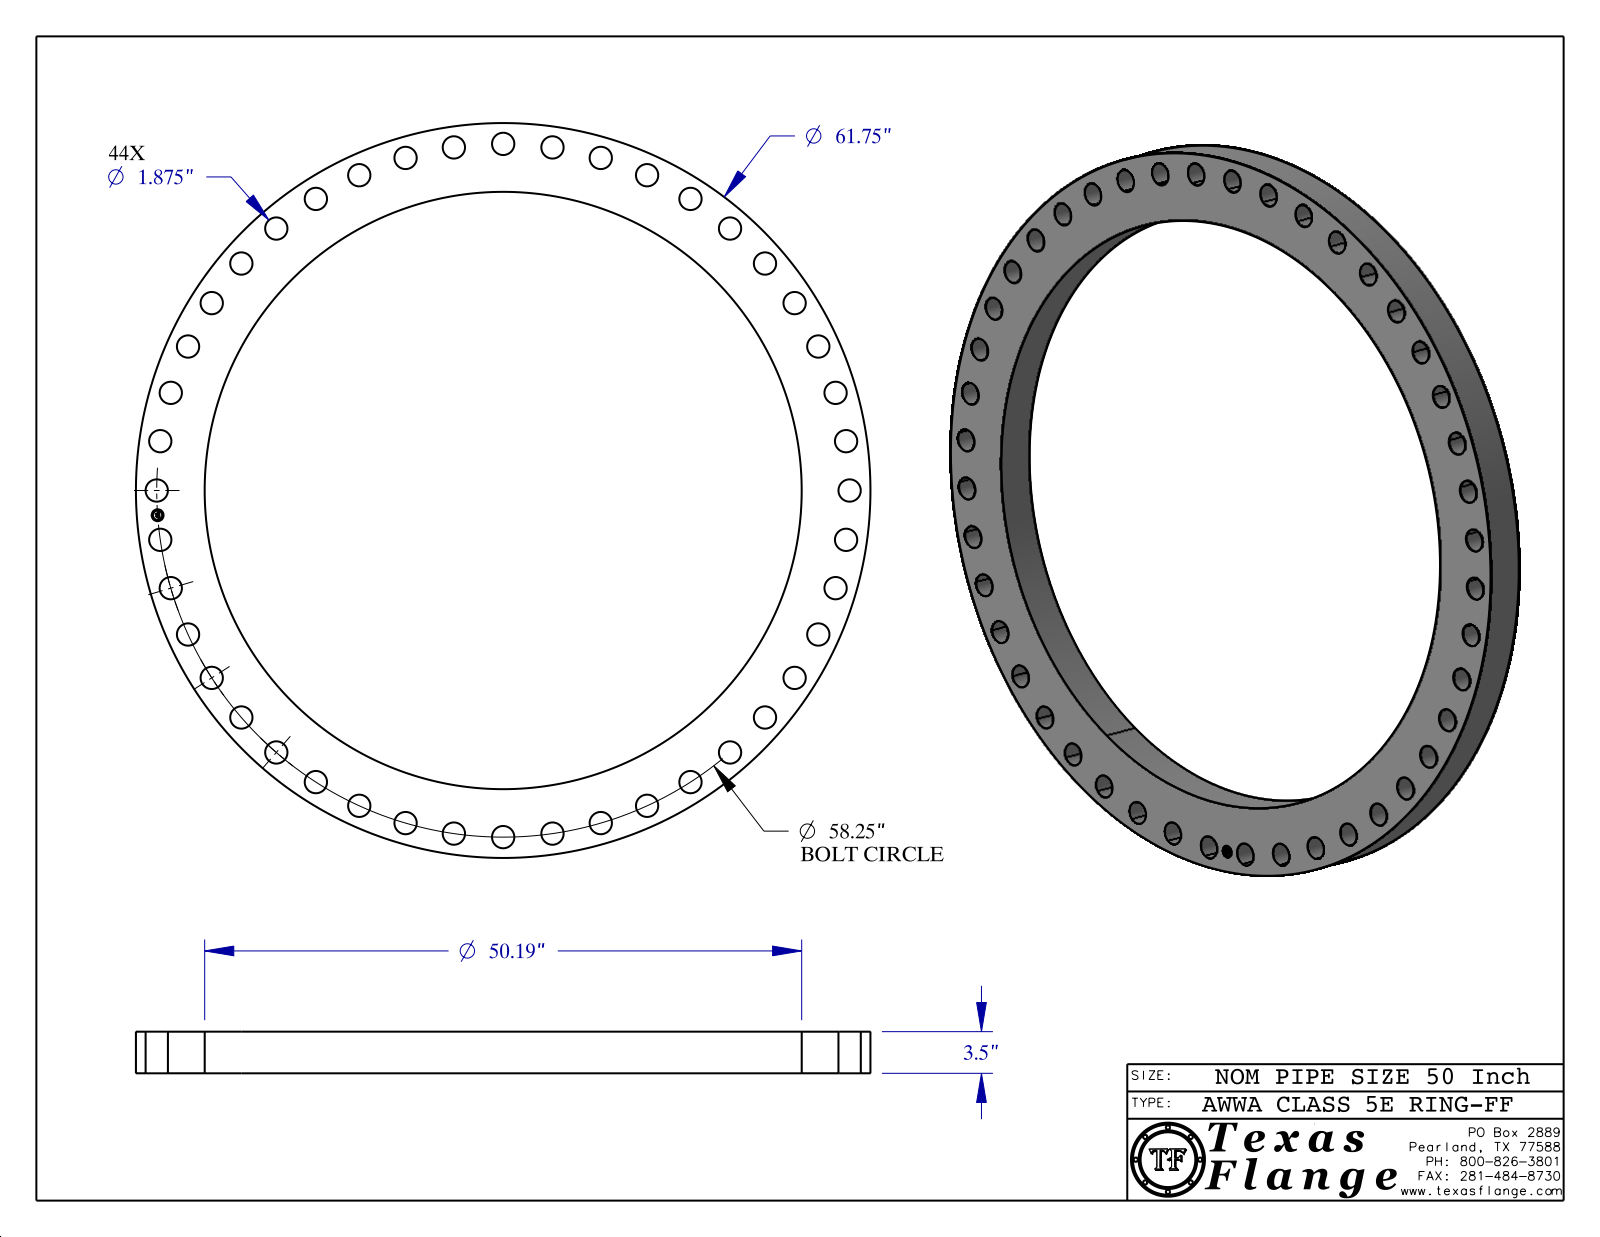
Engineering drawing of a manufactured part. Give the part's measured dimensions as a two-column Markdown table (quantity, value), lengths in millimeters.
| quantity | value |
| --- | --- |
| part name | AWWA Class 5E-RING-FF |
| STEP written by | CATIA V5 STEP AP214 (AUTOMOTIVE_DESIGN) |
| units | millimeters |
| bodies | 1 solid, 479 faces (367 planar, 112 cylindrical, 0 other) |
| overall size | 1568.5 × 1568.5 × 88.9 |
| volume | 51 320 000 mm³ |
| surface area | 2 534 000 mm² |
| round holes (diameter × count) | 47.6 × 44, 25.4 × 1, 1274.8 × 1 |
| round bosses / shafts (diameter × count) | 1.5 × 8, 1568.5 × 1, 20 × 1 |
| main face-to-face distances | 88.9, 88.5, 0.4, 7.6, 7.4, 1.4, 4.9, 6.3, 1.1, 3.8 |
| hole center spacings | 314.5, 517, 210.6, 105.6, 739.8, 416.8, 614.6, 1298.6 |
